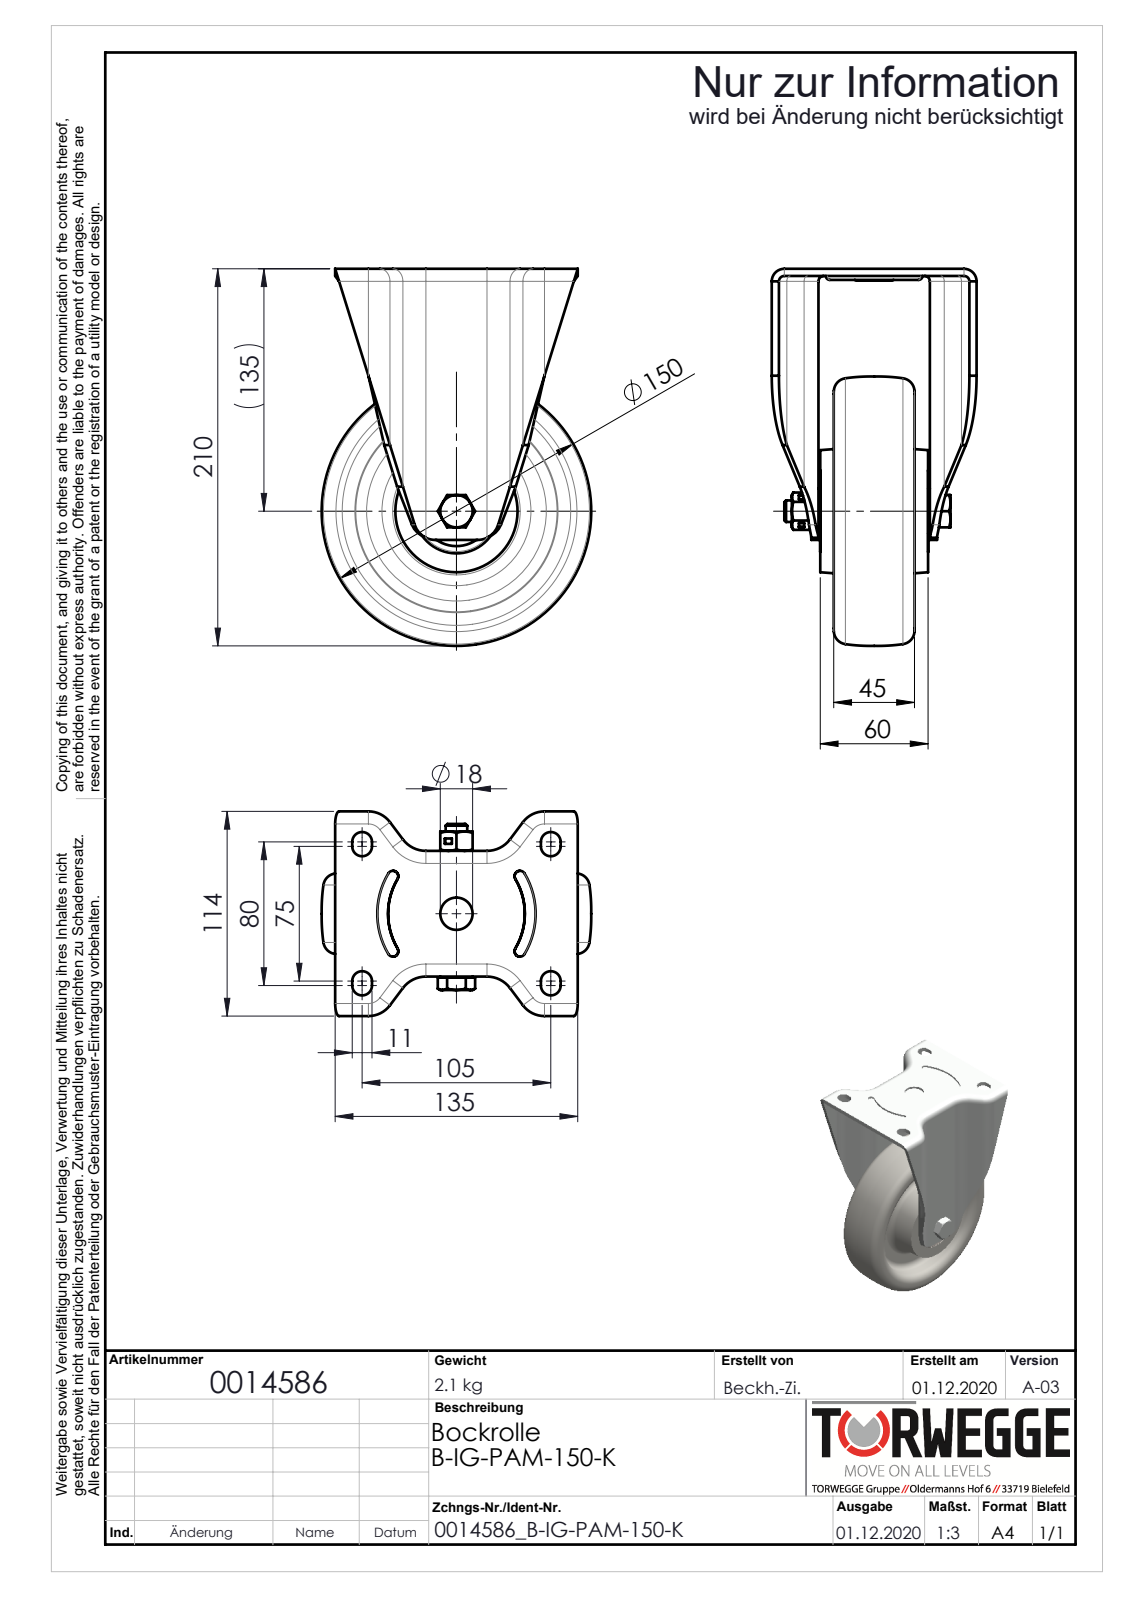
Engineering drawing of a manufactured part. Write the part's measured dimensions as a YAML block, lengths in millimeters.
part_name: "0014586"
step_written_by: "SolidWorks 2018 (AUTOMOTIVE_DESIGN)"
units: millimeters
bodies: {solids: 17, faces: 422, planar: 116, cylindrical: 136, other: 170}
overall_size: [210.02, 150.04, 114]
volume: 767549
surface_area: 204228
round_holes:
  - {diameter: 10.2, count: 1}
  - {diameter: 12, count: 1}
  - {diameter: 12.2, count: 1}
  - {diameter: 12.5, count: 1}
  - {diameter: 18, count: 1}
  - {diameter: 20, count: 1}
  - {diameter: 21, count: 1}
  - {diameter: 28.1, count: 1}
  - {diameter: 35, count: 1}
  - {diameter: 38.9, count: 1}
round_bosses_or_shafts:
  - {diameter: 47, count: 1}
  - {diameter: 28, count: 1}
  - {diameter: 25, count: 1}
  - {diameter: 19.9, count: 1}
  - {diameter: 18, count: 1}
partial_cylinders:
  - {radius: 3, count: 12}
  - {radius: 5.5, count: 8}
  - {radius: 7, count: 8}
  - {radius: 2.2, count: 4}
  - {radius: 11, count: 4}
  - {radius: 15, count: 4}
  - {radius: 16, count: 4}
  - {radius: 20, count: 4}
face_to_face_distances: [4, 66, 2, 26, 62, 30, 40, 36, 70, 1]
